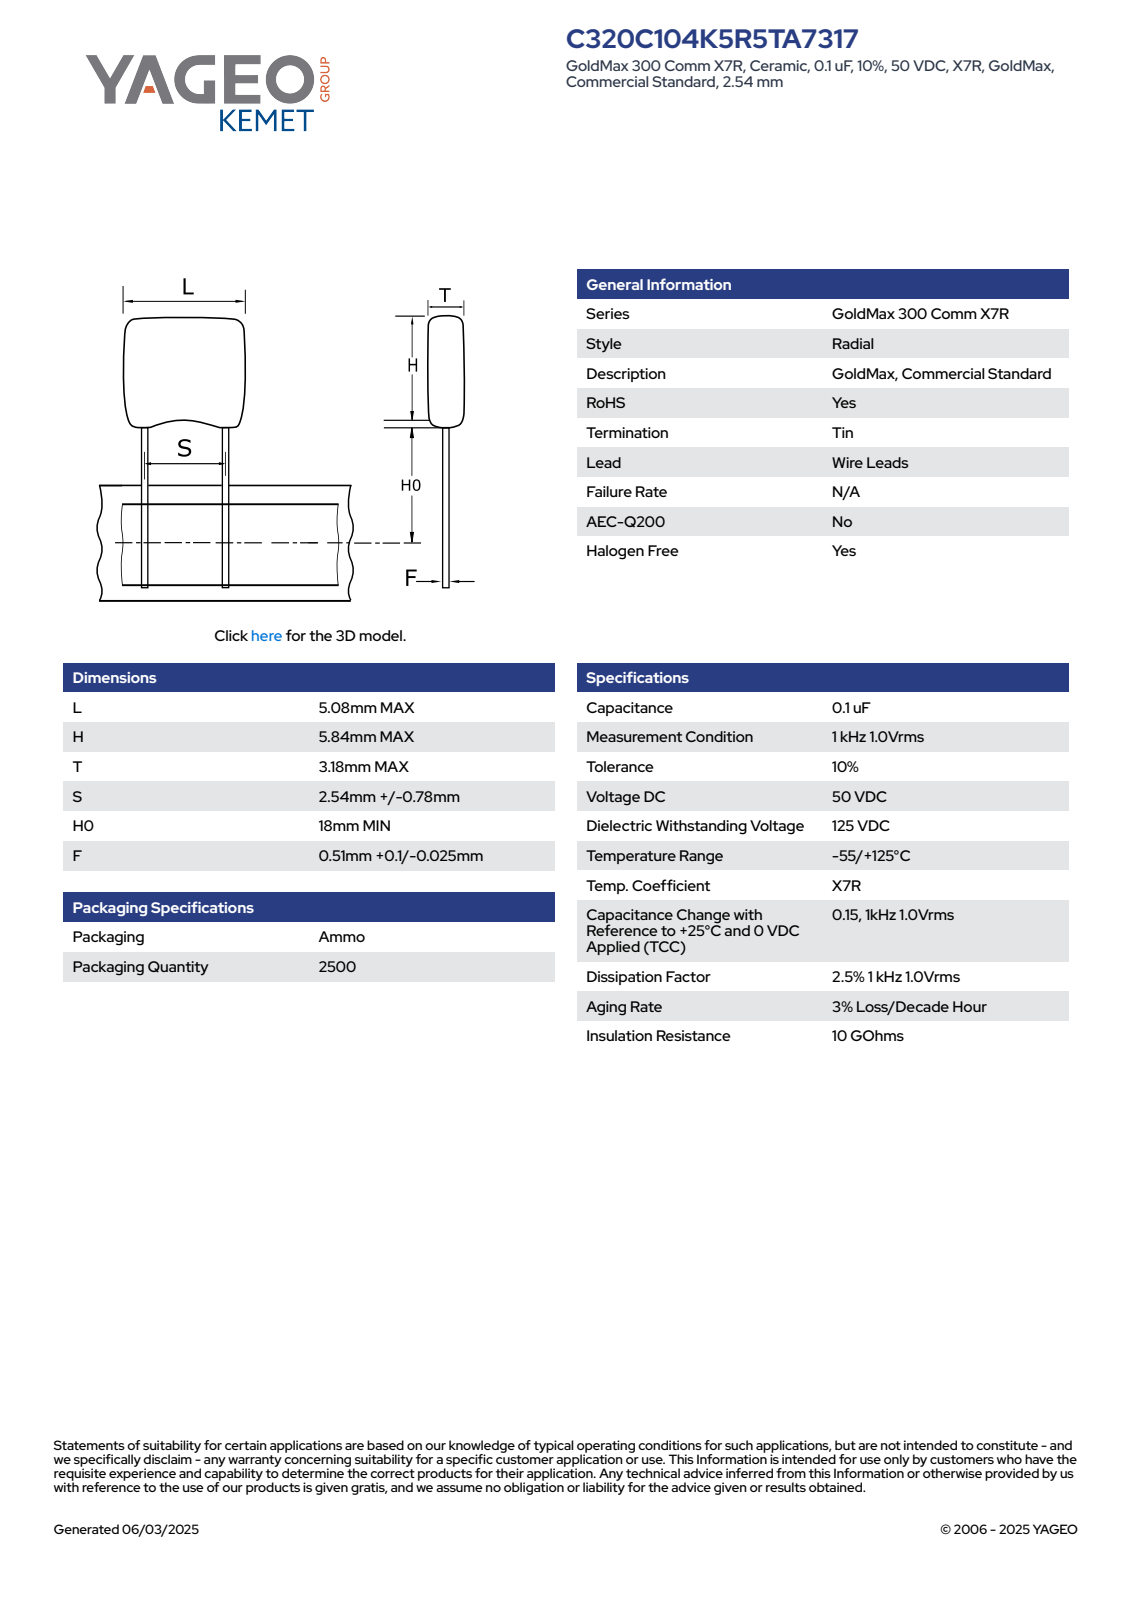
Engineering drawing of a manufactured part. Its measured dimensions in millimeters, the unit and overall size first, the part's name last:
Units: millimetres
Overall size (bounding box): 24.51 × 5.08 × 3.19
Round bosses / shafts (diameter × count): ⌀0.61 ×2
Partial cylindrical surfaces — rounded edges, fillets, slot ends (radius × count): R0.75 ×10
Main face-to-face distances: 3.18, 5.08, 6.51, 18, 24.51, 3.19, 0.54, 21.43, 3.43, 3.08
Volume: 110 mm³ · Surface area: 193 mm²
Bodies: 4 solids, 83 faces (65 planar, 14 cylindrical, 4 other)
Part name (STEP PRODUCT): CCR_KRCST_5.08X5.84_L5.08H5.84T3.18S2.54H018F0.61
STEP written by: SolidWorks 2014 (AUTOMOTIVE_DESIGN)
